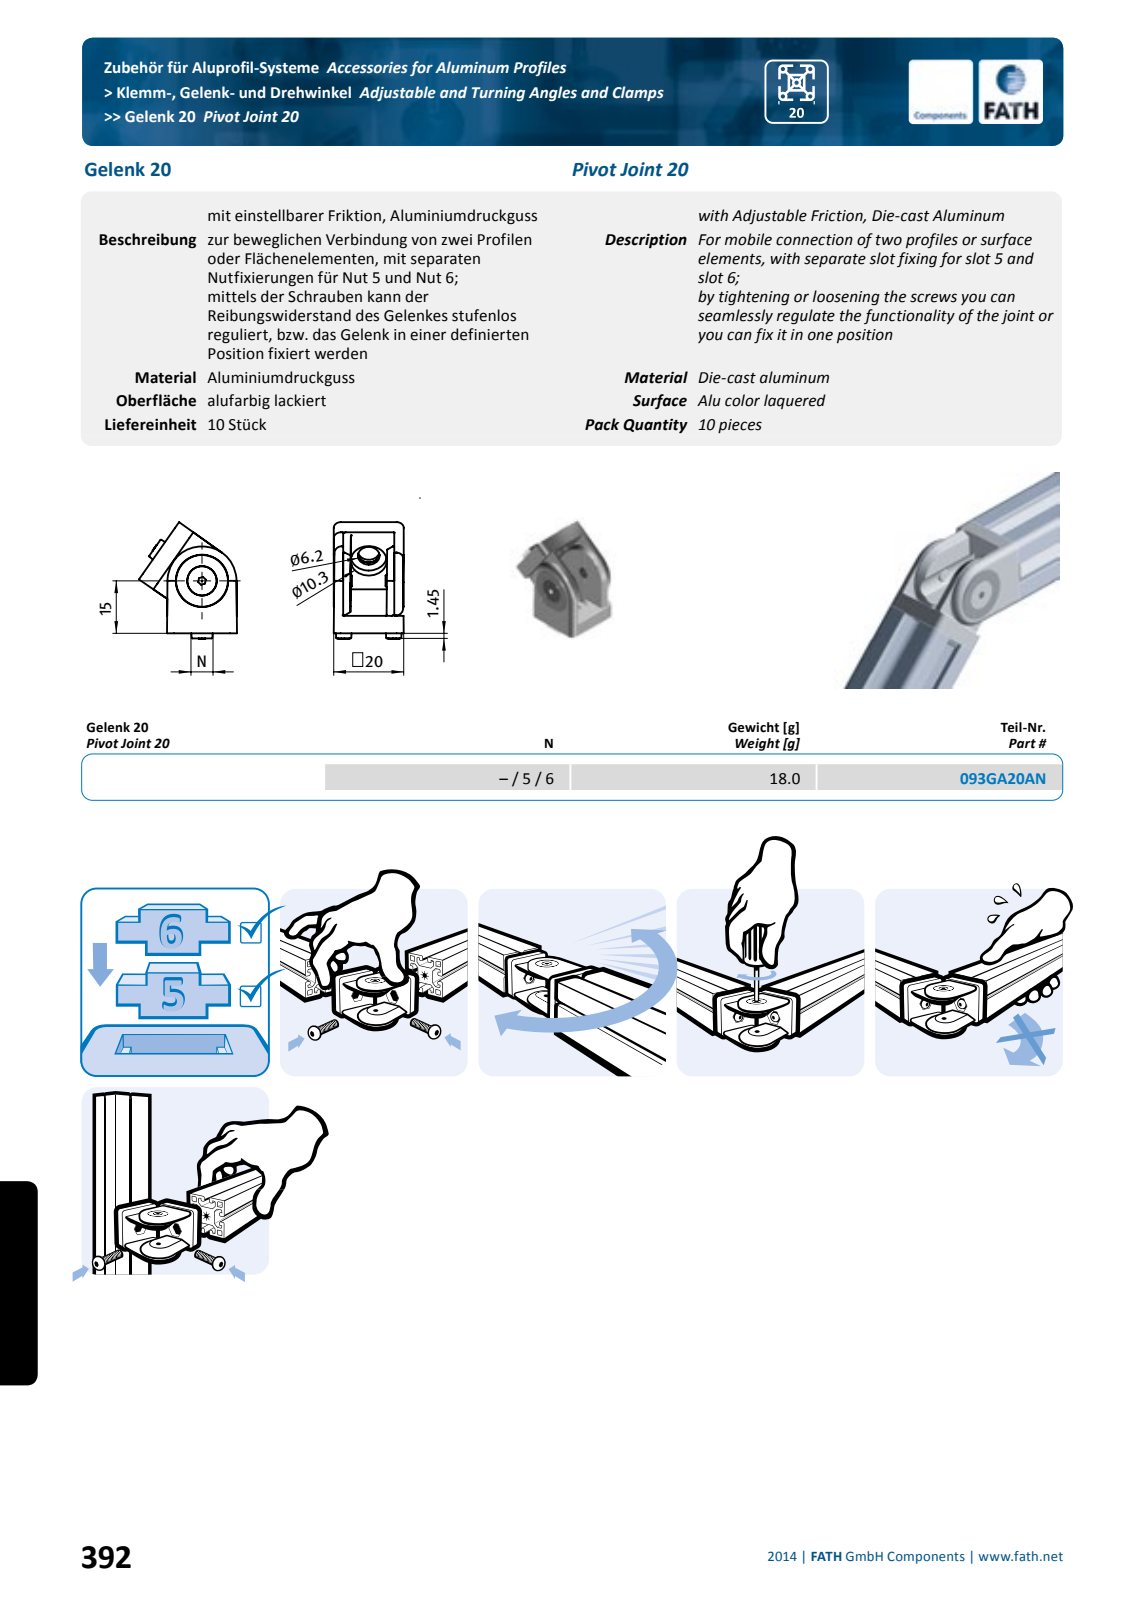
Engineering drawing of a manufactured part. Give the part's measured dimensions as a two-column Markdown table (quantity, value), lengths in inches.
| quantity | value |
| --- | --- |
| part name | fath_093ga20an_1; fath_093ga20an_2; fath_093ga20an_3; fath_093ga20an_4 (+6 more) |
| STEP written by | Spatial InterOp 3D (automotive_design) |
| units | inches |
| bodies | 10 solids, 516 faces (248 planar, 136 cylindrical, 132 other) |
| overall size | 1.38 × 1.087 × 0.787 |
| volume | 0.411 in³ |
| surface area | 12.07 in² |
| round holes (diameter × count) | 0.059 × 4, 0.244 × 3, 0.406 × 2, 0.319 × 1, 0.433 × 1, 0.551 × 1, 0.673 × 1 |
| round bosses / shafts (diameter × count) | 0.777 × 1, 0.669 × 1, 0.547 × 1, 0.429 × 1, 0.315 × 1, 0.157 × 1 |
| partial cylindrical surfaces (radius × count) | 0.008 × 30, 0.02 × 8, 0.079 × 8 |
| main face-to-face distances | 0.02, 0.551, 0.039, 0.142, 0.571, 0.531, 0.591, 0.055, 0.197, 0.569 |
| hole center spacings | 0.276, 0.189, 0.518, 0.551 |
